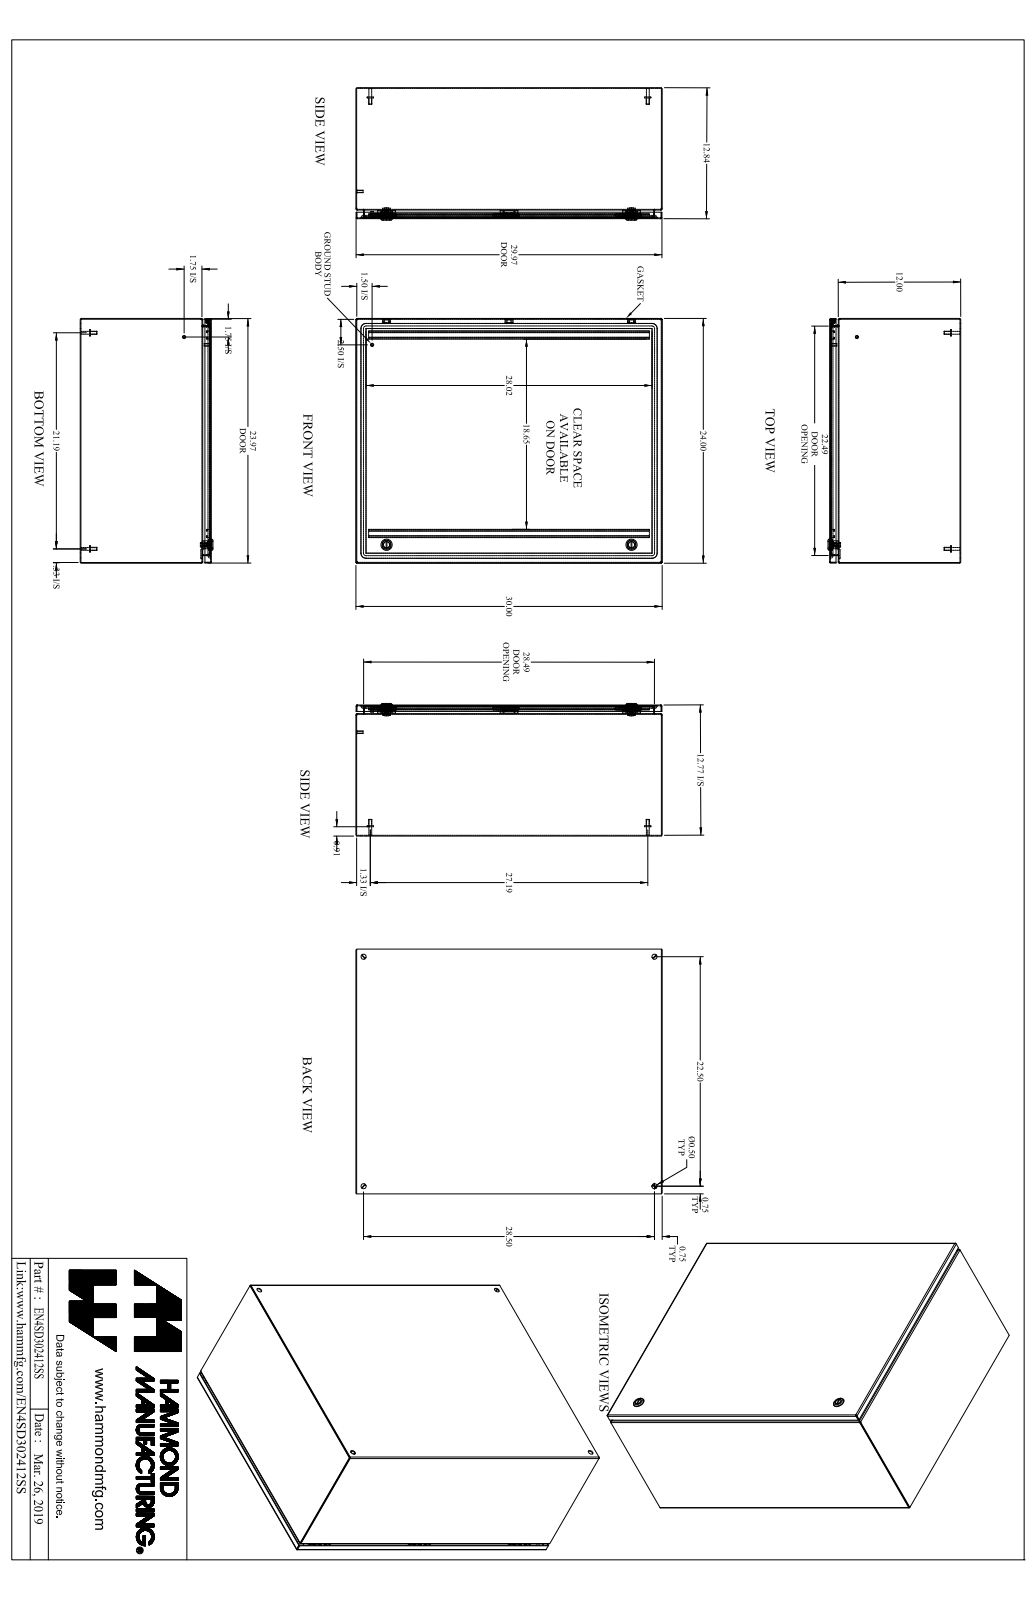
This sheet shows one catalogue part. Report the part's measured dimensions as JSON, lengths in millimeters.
{"part_name": "EN4SD302412SS", "step_written_by": "SolidWorks 2019 (AUTOMOTIVE_DESIGN)", "units": "millimeters", "bodies": {"solids": 35, "faces": 876, "planar": 419, "cylindrical": 297, "other": 160}, "overall_size": [762, 609.6, 330.3], "volume_mm3": 3708000, "surface_area_mm2": 4102000, "round_holes": [[12.7, 6], [5, 2], [9.8, 2], [16, 2], [19.5, 2], [4.4, 1], [6.1, 1], [6.1, 1]], "round_bosses_or_shafts": [[15.9, 6], [8, 6], [7, 4], [27.9, 2], [19.9, 2], [13.3, 2], [6.4, 2], [6, 2]], "partial_cylinders_radius": [[0.9, 14], [2.7, 14], [0.3, 12], [1.2, 12], [7.9, 12], [2.5, 8], [0.2, 6], [1.6, 6]], "face_to_face_distances": [1.8, 324.4, 322.5, 326.2, 607.8, 760.2, 605.9, 609.6, 758.3, 762], "hole_center_spacings": [547.5, 571.5, 723.9, 922.3, 63.2, 63.2, 609.6, 667.3]}
